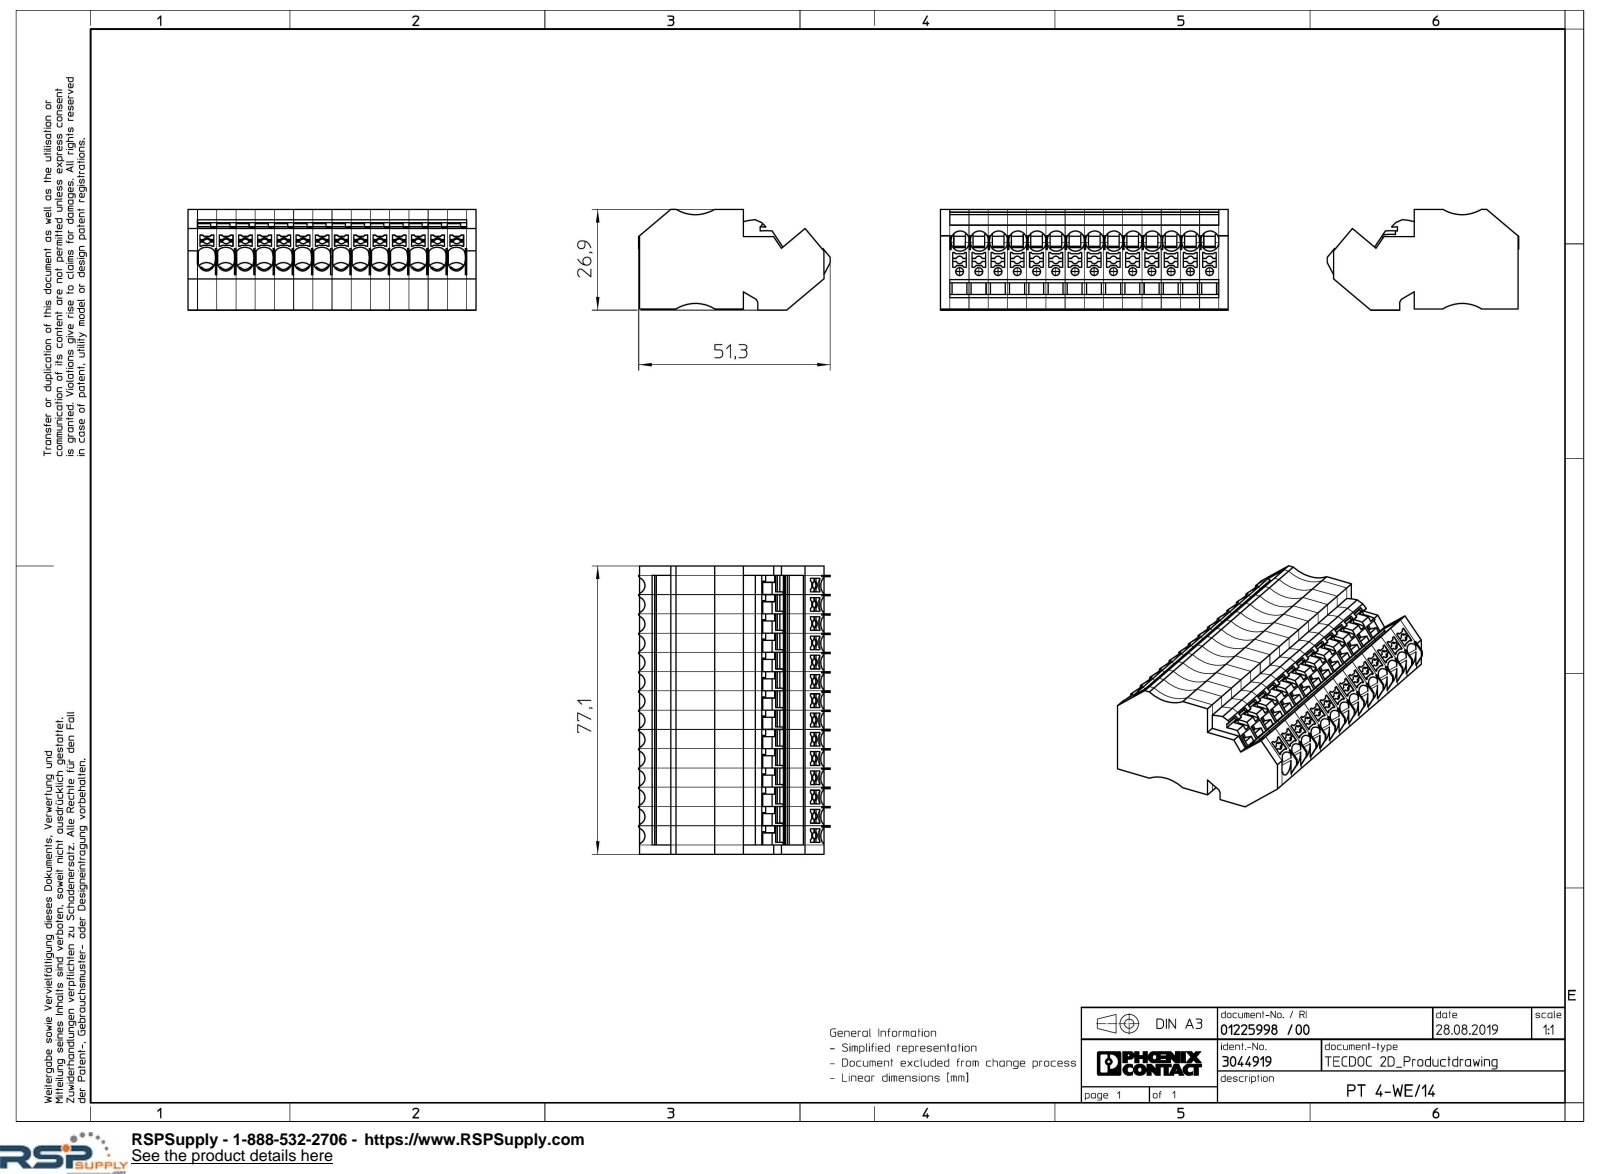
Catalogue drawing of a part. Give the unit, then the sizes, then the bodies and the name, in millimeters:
Units: millimetres
Overall size (bounding box): 77.1 × 51.3 × 26.9
Round holes (diameter × count): ⌀2.1 ×14
Partial cylindrical surfaces — rounded edges, fillets, slot ends (radius × count): R2.4 ×56, R1 ×28, R1.03 ×3, R10 ×2, R1.05 ×1, R1.78 ×1, R12.4 ×1, R13.38 ×1
Main face-to-face distances: 77.1, 3.15, 3.85, 7, 5.15, 15.45, 10.3, 27.8, 19.6, 26.6
Hole centre spacings: 5.15, 10.3, 15.45, 20.6, 25.75, 30.9, 36.05, 41.2
Volume: 69 480 mm³ · Surface area: 26 892 mm²
Bodies: 1 solid, 2347 faces (2035 planar, 284 cylindrical, 28 other)
Part name (STEP PRODUCT): PT_4_WE_14-select
STEP written by: Creo Elements/Direct Modeling 20.1A 29-Sep-2018 (C) Parametric Technology GmbH (AUTOMOTIVE_DESIGN)
